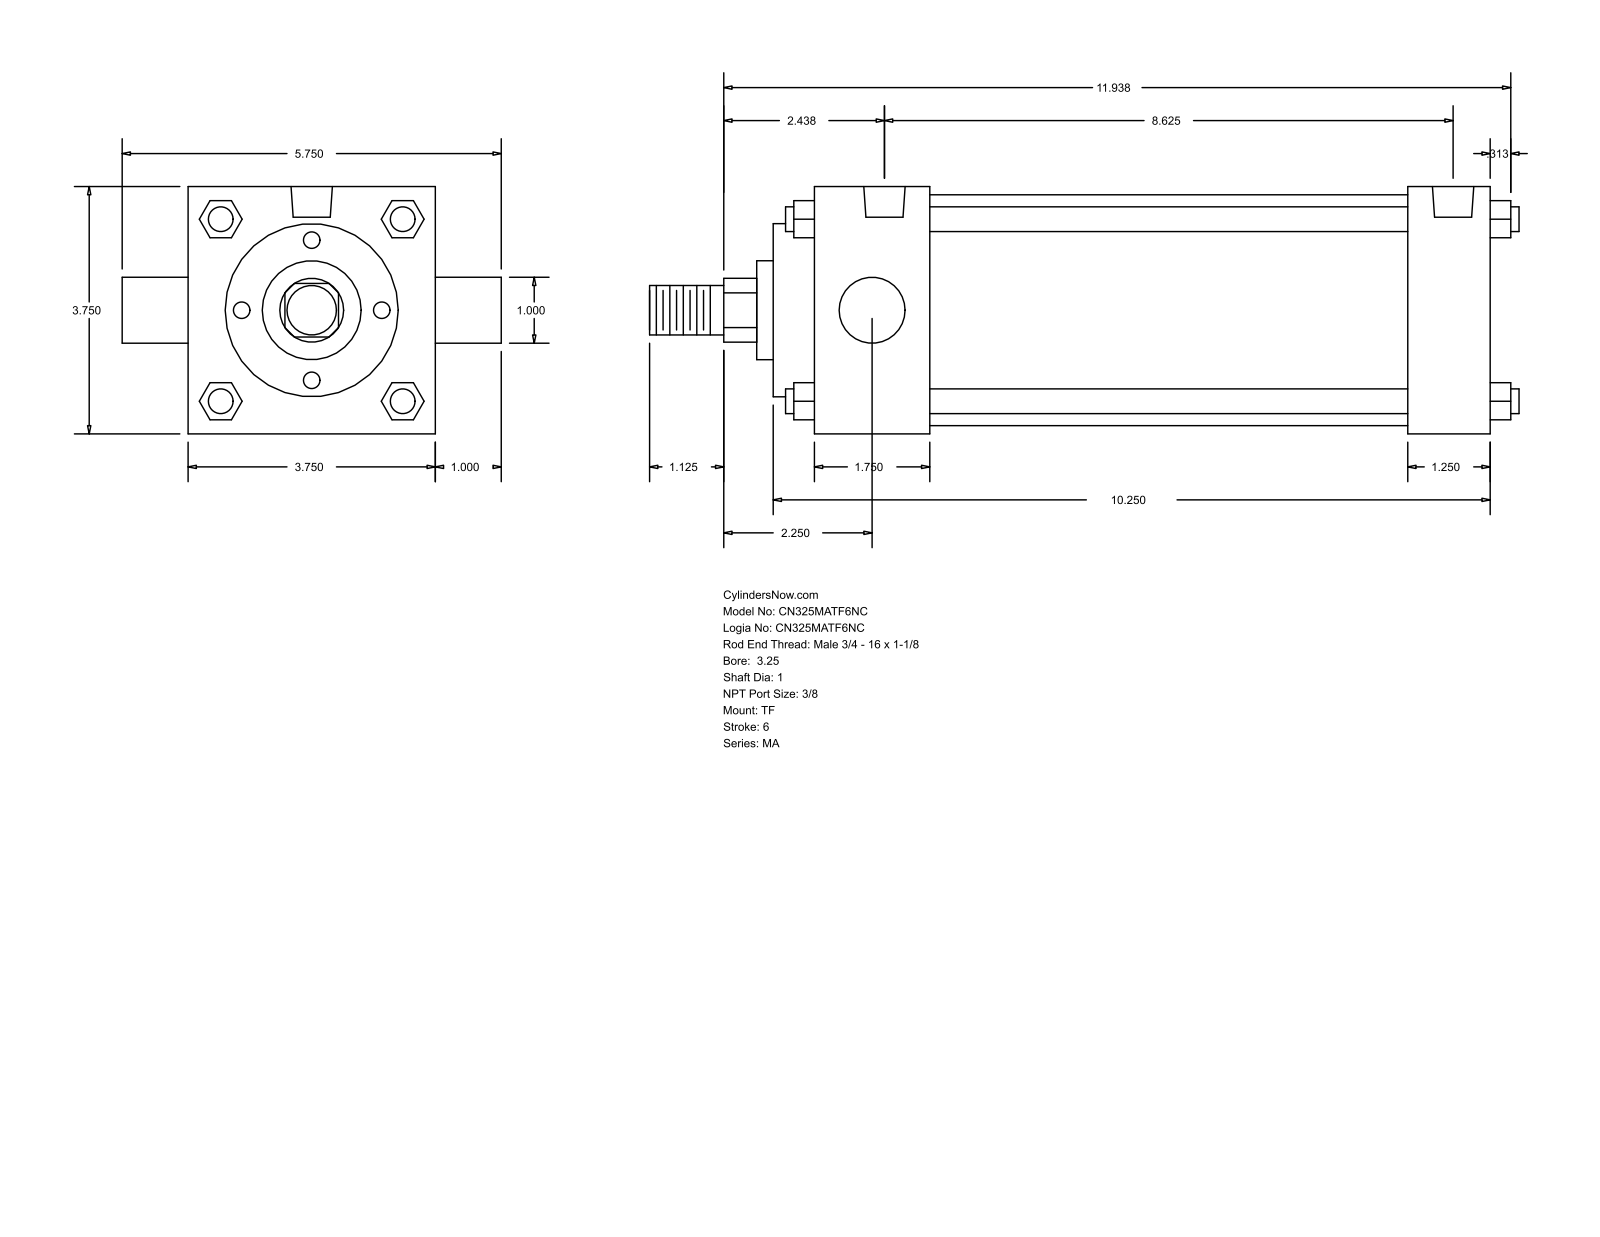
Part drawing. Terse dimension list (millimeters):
name: MA_TF__0325_1
written by: GSSL Pune (CONFIG_CONTROL_DESIGN)
unit: mm
bodies: 0 solids, 122 faces (93 planar, 29 cylindrical, 0 other)
size: 334.96 × 146.05 × 95.25
holes: 3× ⌀11.11, 2× ⌀15.93
bosses: 4× ⌀9.53, 2× ⌀25.4, 1× ⌀88.9, 1× ⌀66.67, 1× ⌀38.1, 1× ⌀19.05
rounds: 1× R12.29
face distances: 95.24, 260.35, 276.22, 44.46, 228.6, 184.14, 215.89, 31.75, 15.87, 60.33
hole spacings: 4.76, 214.32, 209.56, 219.08
